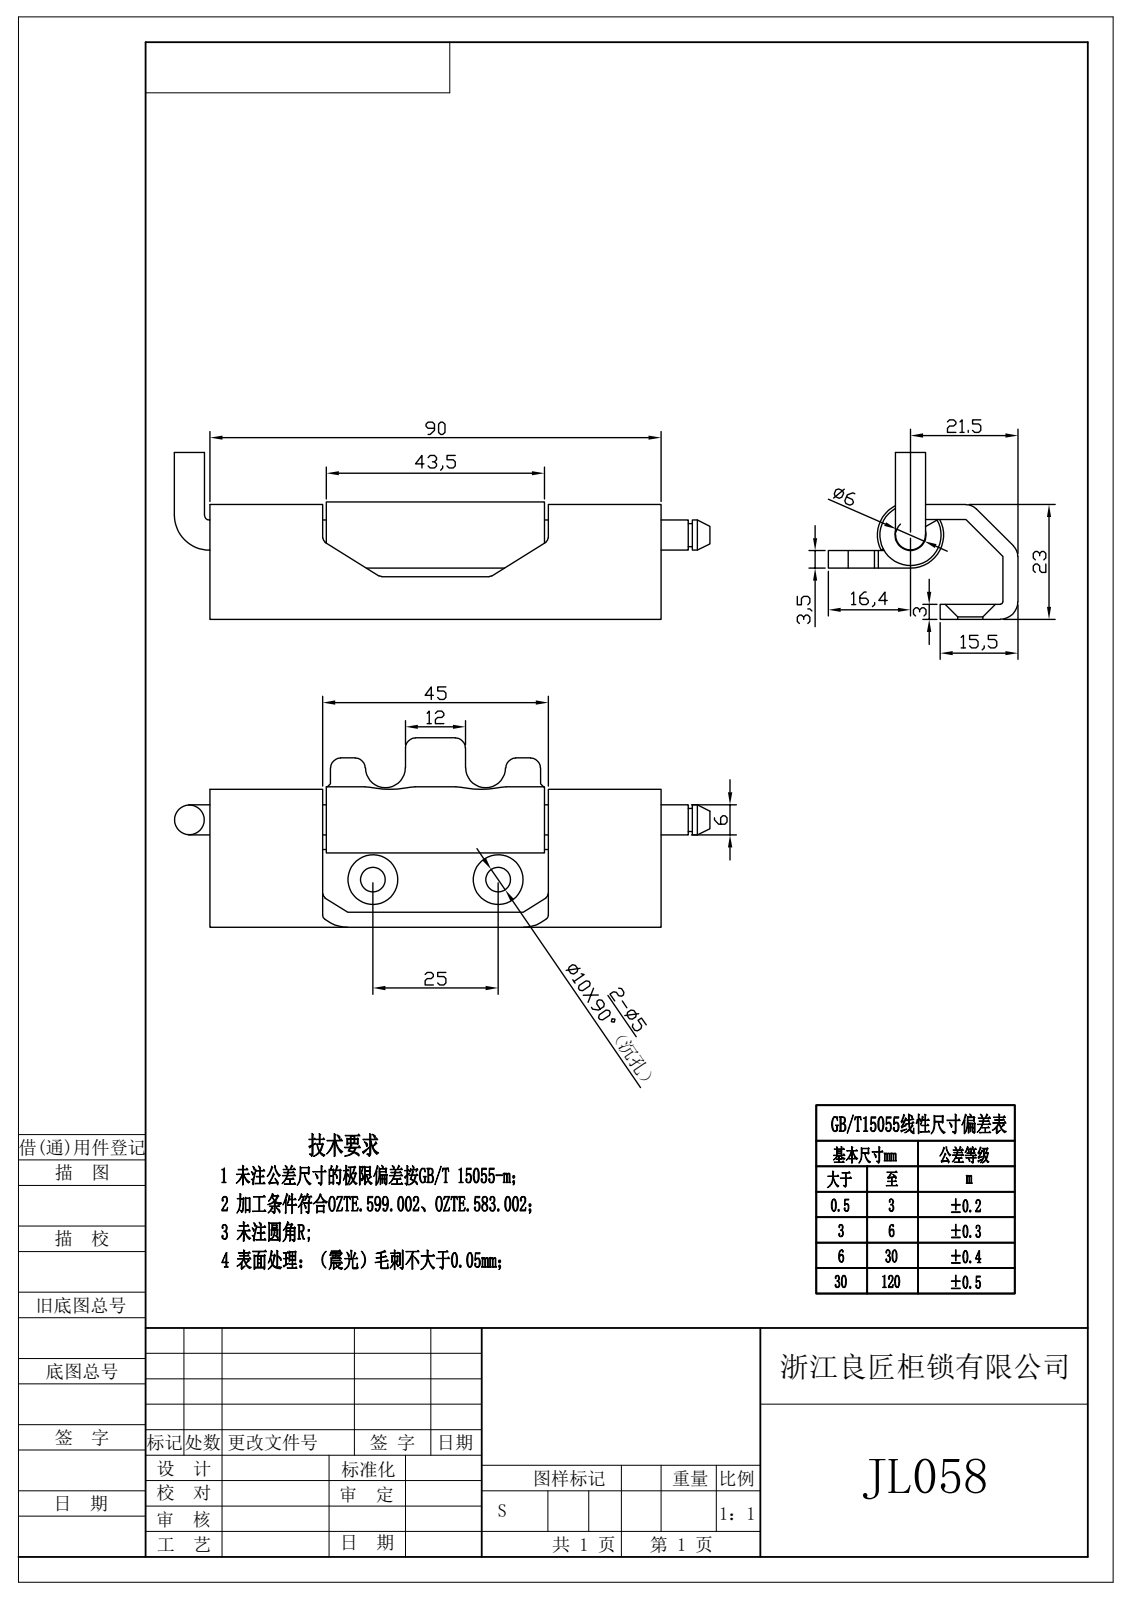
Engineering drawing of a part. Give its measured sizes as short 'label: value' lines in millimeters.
written by: Rhino 8.5 (CONFIG_CONTROL_DESIGN)
unit: mm
bodies: 3 solids, 105 faces (46 planar, 47 cylindrical, 12 other)
size: 106.8 × 37.82 × 33.32
volume: 21 061 mm³; area: 15 663 mm²
holes: 2× ⌀5, 1× ⌀6.2
bosses: 2× ⌀6, 1× ⌀13.2, 1× ⌀12.2, 1× ⌀4.6
rounds: 6× R1, 6× R2, 4× R1.5, 2× R2.5, 2× R3, 2× R4, 2× R6.3, 1× R0.5
face distances: 3, 19.92, 3.5, 22.92, 16.92, 13.72, 10.72, 6.2, 9.2, 10.22
hole spacings: 25
